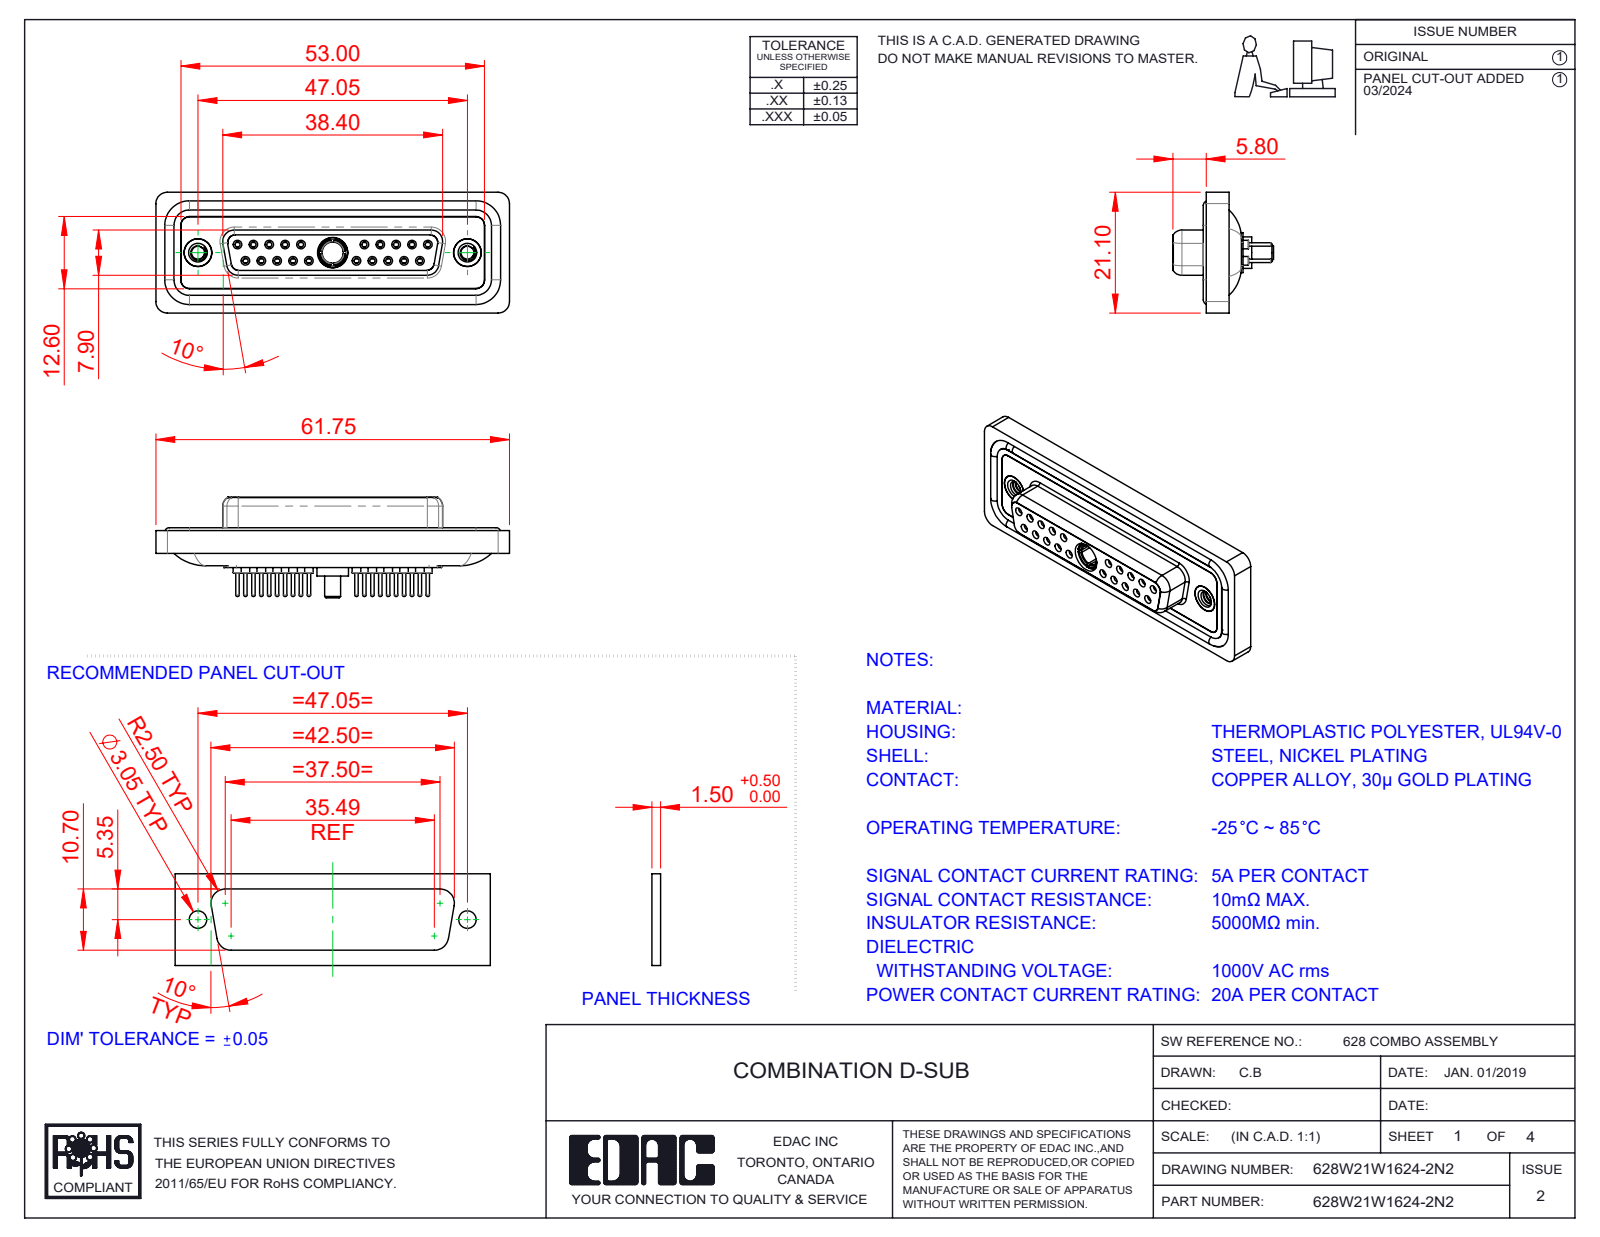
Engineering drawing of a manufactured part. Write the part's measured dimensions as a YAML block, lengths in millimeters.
part_name: "Power Socket_20A S; 628Combo Contact Row 1_24; 628Combo Threaded Rivet_2; 628Combo Contact Row 2_24 (+5 more)"
step_written_by: "SolidWorks 2023 (CONFIG_CONTROL_DESIGN)"
units: millimeters
bodies: {solids: 29, faces: 1560, planar: 434, cylindrical: 591, other: 535}
overall_size: [61.75, 21.1, 17.55]
volume: 8374
surface_area: 14002
round_holes:
  - {diameter: 0.9, count: 20}
  - {diameter: 1.1, count: 20}
  - {diameter: 1.5, count: 20}
  - {diameter: 2, count: 20}
  - {diameter: 1.6, count: 10}
  - {diameter: 1.7, count: 10}
  - {diameter: 4.85, count: 3}
  - {diameter: 2.26, count: 2}
  - {diameter: 4, count: 2}
  - {diameter: 4.05, count: 2}
  - {diameter: 5, count: 2}
  - {diameter: 3.7, count: 1}
round_bosses_or_shafts:
  - {diameter: 2.2, count: 20}
  - {diameter: 0.6, count: 20}
  - {diameter: 1.6, count: 14}
  - {diameter: 4.95, count: 2}
  - {diameter: 4.8, count: 2}
  - {diameter: 5.5, count: 1}
  - {diameter: 5.2, count: 1}
  - {diameter: 4.96, count: 1}
partial_cylinders:
  - {radius: 1.5, count: 22}
  - {radius: 2, count: 18}
  - {radius: 1.35, count: 8}
  - {radius: 1.6, count: 8}
  - {radius: 0.25, count: 4}
  - {radius: 0.5, count: 4}
  - {radius: 0.6, count: 4}
  - {radius: 0.65, count: 4}
face_to_face_distances: [0.4, 1.8, 7.45, 6.6, 5.65, 0.5, 1.6, 7.05, 2.9, 1.1]
hole_center_spacings: [3.16, 2.77, 5.54, 5.03, 8.31, 7.48, 16.62, 19.39]
